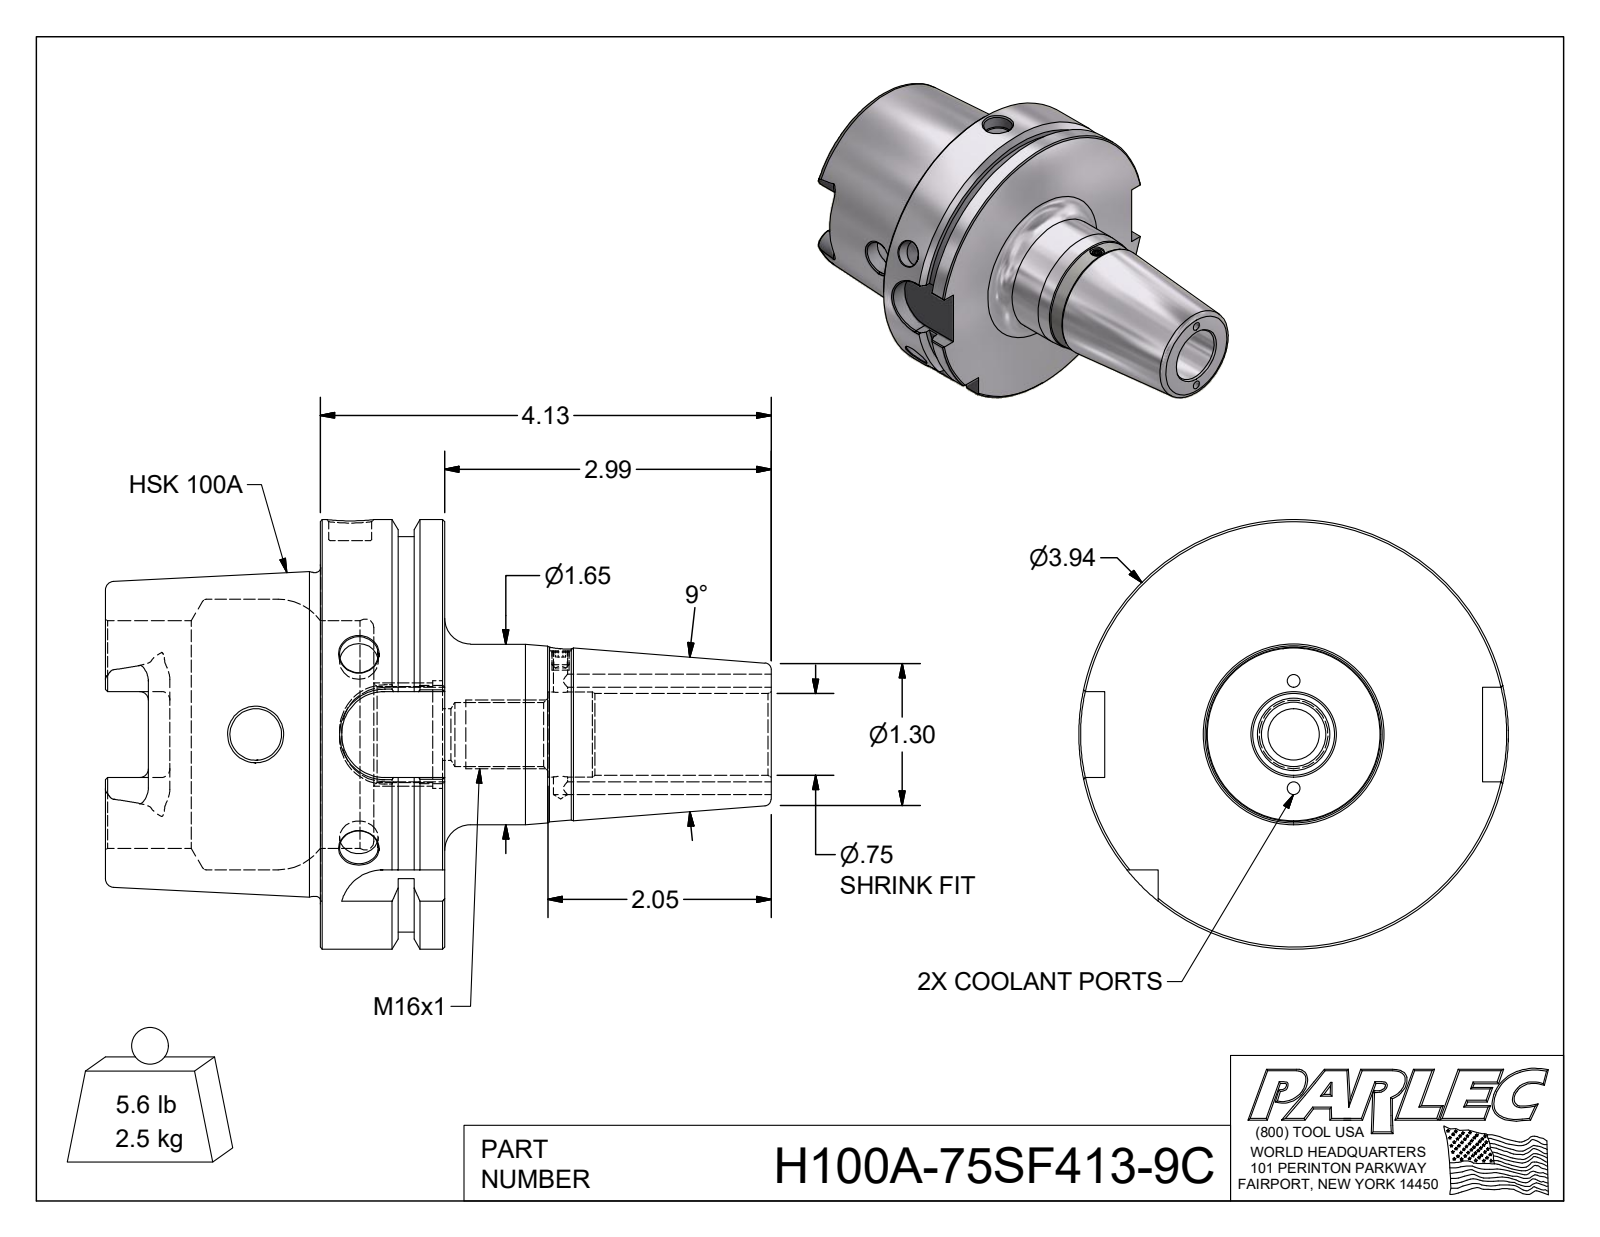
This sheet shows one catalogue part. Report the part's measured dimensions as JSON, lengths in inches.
{"step_written_by": "Autodesk Inventor 2018 (AUTOMOTIVE_DESIGN)", "units": "inches", "bodies": {"solids": 1, "faces": 153, "planar": 49, "cylindrical": 42, "other": 62}, "overall_size": [6.102, 3.937, 3.937], "volume_in3": 19.79, "surface_area_in2": 98.26, "round_holes": [[0.118, 2], [0.354, 2], [0.472, 2], [0.128, 1], [0.197, 1], [0.394, 1], [0.587, 1], [0.749, 1], [0.779, 1], [0.881, 1], [0.985, 1], [2.087, 1]], "round_bosses_or_shafts": [[3.937, 1], [3.622, 1], [2.967, 1], [1.654, 1]], "partial_cylinders_radius": [[0.079, 6], [0.192, 4], [0.394, 4]], "face_to_face_distances": [1.142, 0.492, 0.65, 1.969, 2.461, 3.11, 3.465, 2.83, 0.861, 0.369], "hole_center_spacings": [0.492, 0.984, 1.928]}
